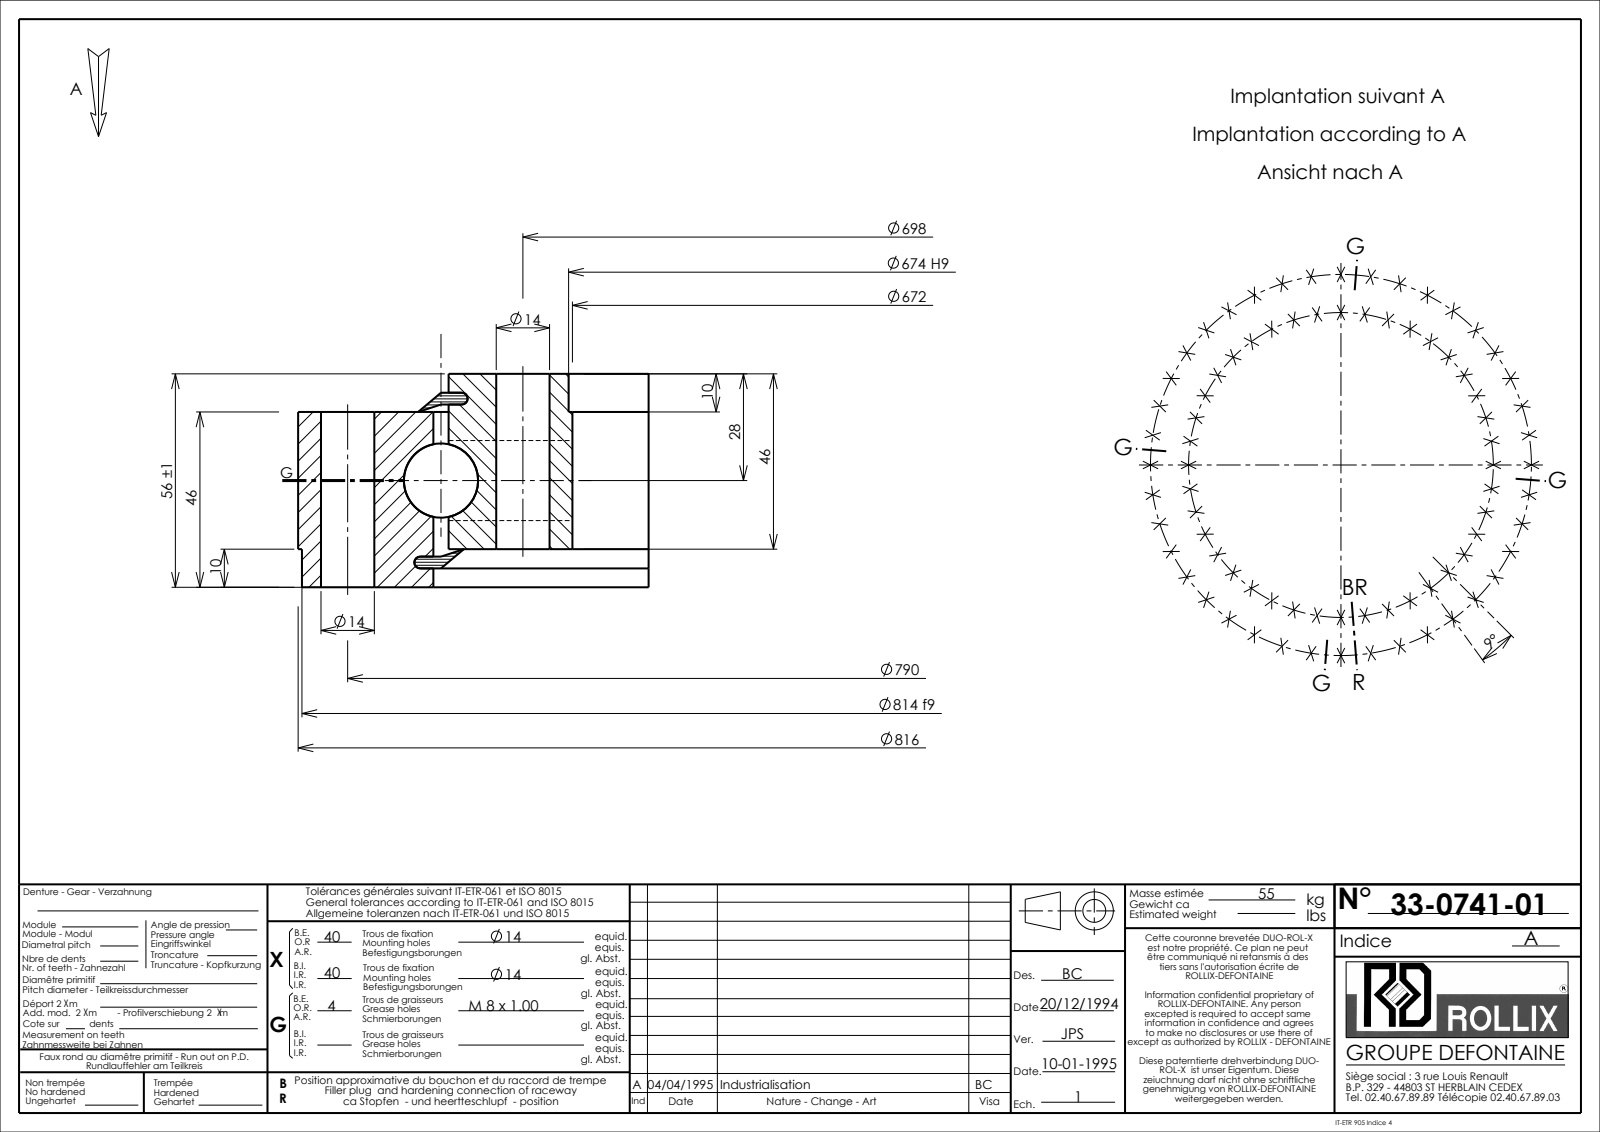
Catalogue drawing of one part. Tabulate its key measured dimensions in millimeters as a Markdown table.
| quantity | value |
| --- | --- |
| part name | 33-0741-01 |
| STEP written by | SolidWorks 2016 (CONFIG_CONTROL_DESIGN) |
| units | millimeters |
| bodies | 9 solids, 318 faces (54 planar, 196 cylindrical, 68 other) |
| overall size | 833.03 × 833.03 × 56 |
| volume | 6 259 000 mm³ |
| surface area | 1 104 000 mm² |
| round holes (diameter × count) | 14 × 80, 7 × 4, 672 × 1, 674 × 1, 745 × 1 |
| round bosses / shafts (diameter × count) | 8 × 4, 816 × 1, 814 × 1, 737 × 1 |
| main face-to-face distances | 46, 10, 36, 56, 8.05, 47.95, 1.95, 37.95, 4.95, 51.05 |
| hole center spacings | 267.11, 109.19, 644.87, 695.85, 54.76, 162.94, 493.56, 364.7 |
